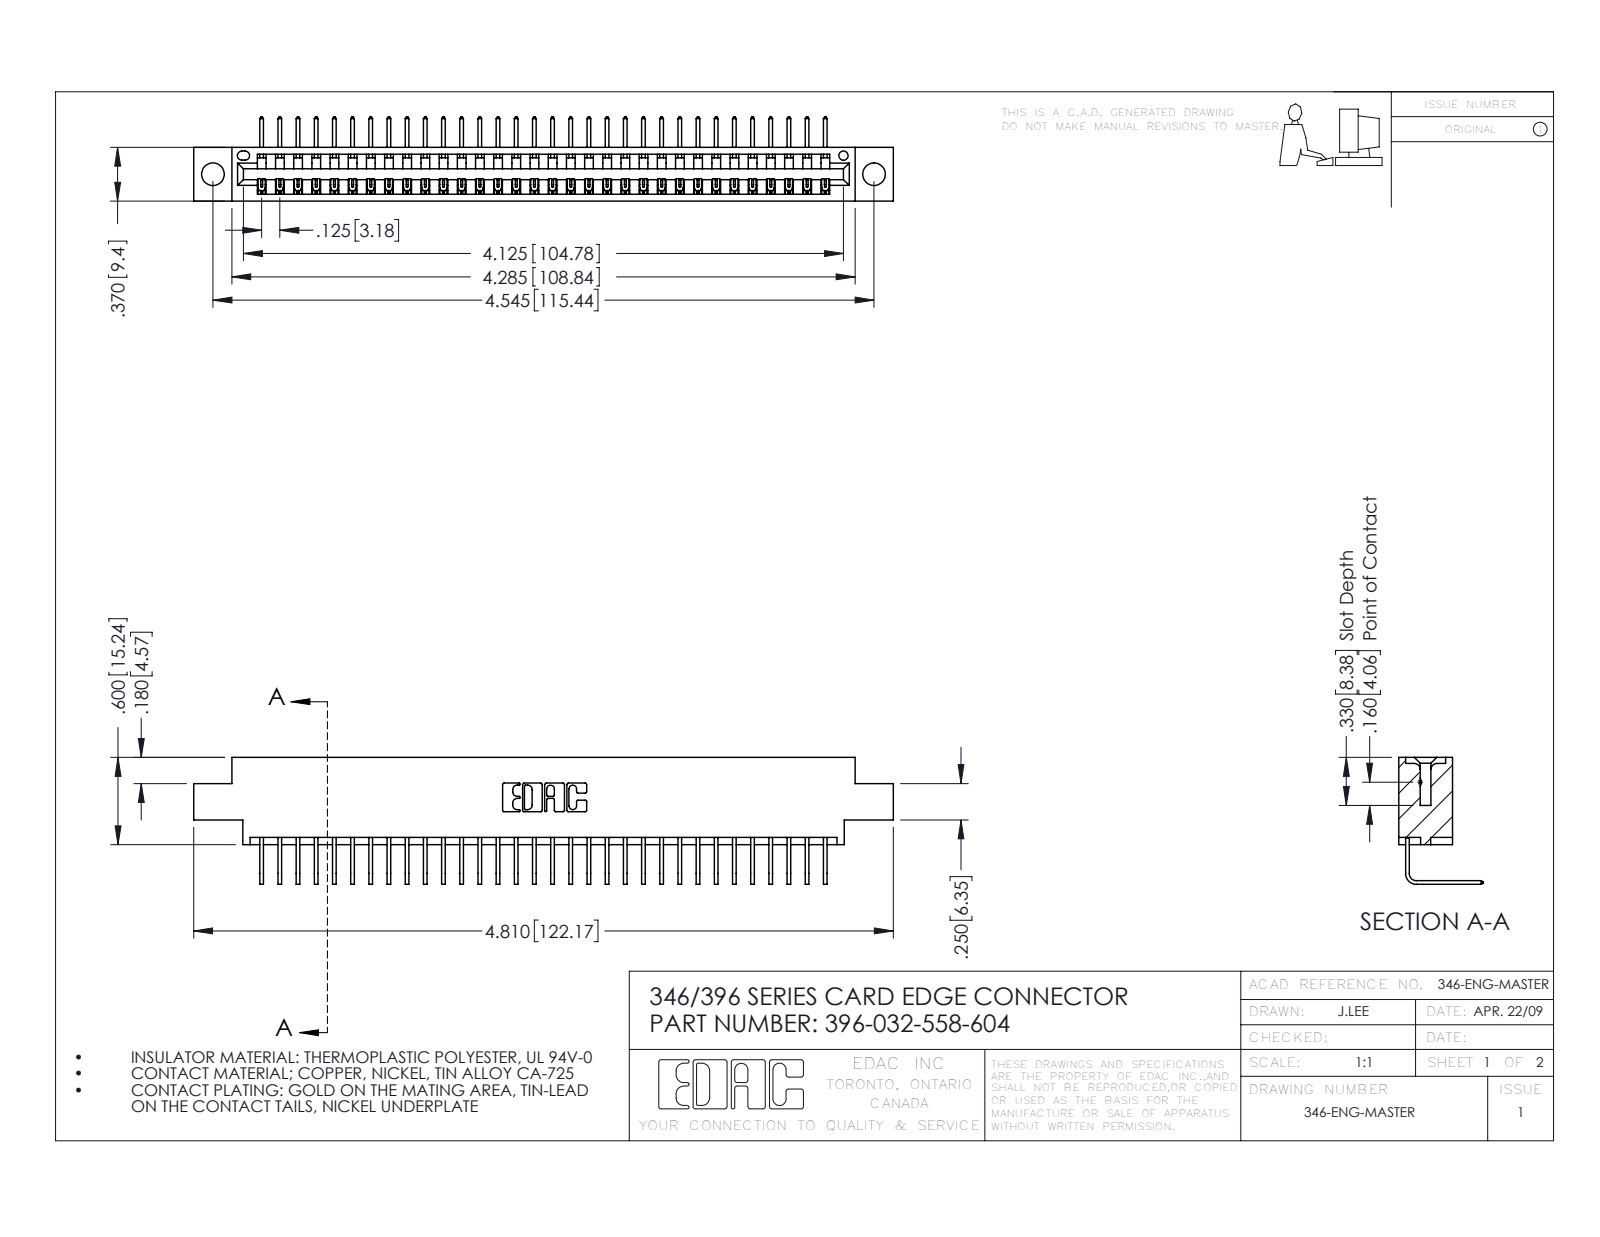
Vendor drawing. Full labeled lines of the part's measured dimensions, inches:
Part name (STEP PRODUCT): 396-032-558-604; 346 Part_0.170 Offset - 0.156 Dia-TH; 345-292-001_558 Tail - 2
STEP written by: SolidWorks 2016 (CONFIG_CONTROL_DESIGN)
Units: inches
Bodies: 33 solids, 2046 faces (1424 planar, 622 cylindrical, 0 other)
Overall size (bounding box): 4.81 × 0.873 × 0.58
Volume: 0.701 in³ · Surface area: 23.02 in²
Round holes (diameter × count): ⌀0.156 ×2, ⌀0.064 ×1
Partial cylindrical surfaces — rounded edges, fillets, slot ends (radius × count): R0.006 ×64, R0.01 ×22, R0.007 ×6, R0.031 ×6, R0.026 ×3, R0.031 ×2, R0.04 ×2, R0.014 ×1
Main face-to-face distances: 0.322, 0.048, 0.37, 0.25, 0.298, 0.025, 0.072, 0.148, 0.222, 0.1
Hole centre spacings: 0.246, 4.337, 4.545
